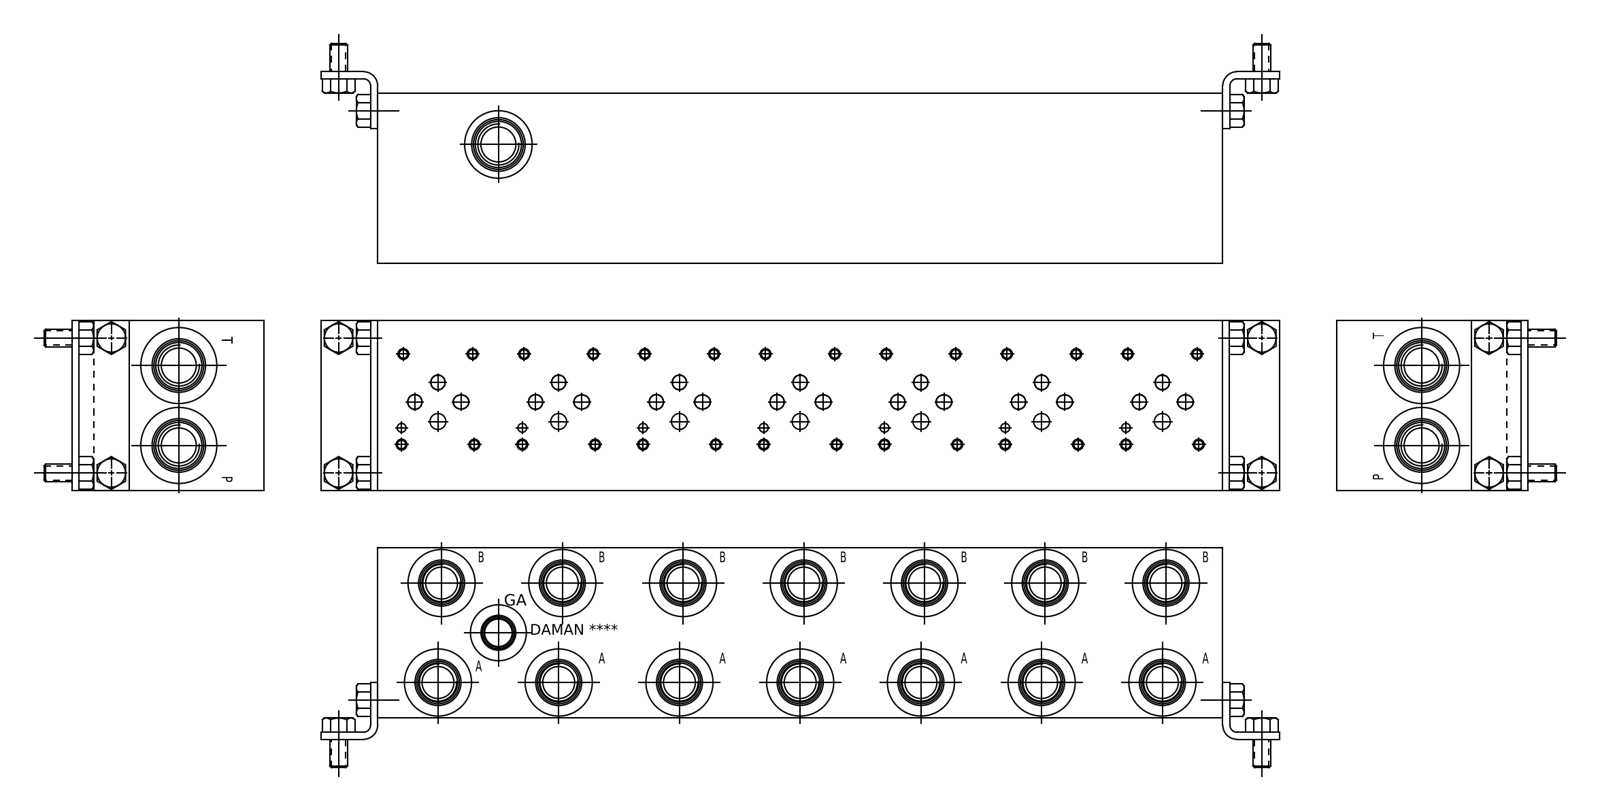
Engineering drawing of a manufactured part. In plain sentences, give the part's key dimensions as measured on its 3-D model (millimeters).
The part is named "Part_AD03S072S~C_3D". Its 3-D file was written by "Autodesk Inventor 2019 (AUTOMOTIVE_DESIGN)". It is 1 solid with 1129 faces: 529 planar, 203 cylindrical and 397 other. Overall it measures 377.82 by 76.2 by 76.2 millimeters. Its volume is 2 030 000 cubic millimeters and its surface area 168 152 square millimeters. Round holes: 28 of diameter 3.78, 28 of diameter 4.83, 21 of diameter 6.35, 14 of diameter 14.3, 14 of diameter 17.5, 14 of diameter 19.05, 14 of diameter 19.25, 14 of diameter 30.63, 7 of diameter 3.96, 7 of diameter 7.14, 2 of diameter 6.53, 2 of diameter 7.92. The main face-to-face distances are 76.2, 0.79, 75.41, 377.82, 377.03, 377.04, 376.25, 0.78, 15.06, 14.27. The hole center spacings are 107.95, 53.97, 53.98, 215.9, 161.92, 161.93, 98, 98.03.
